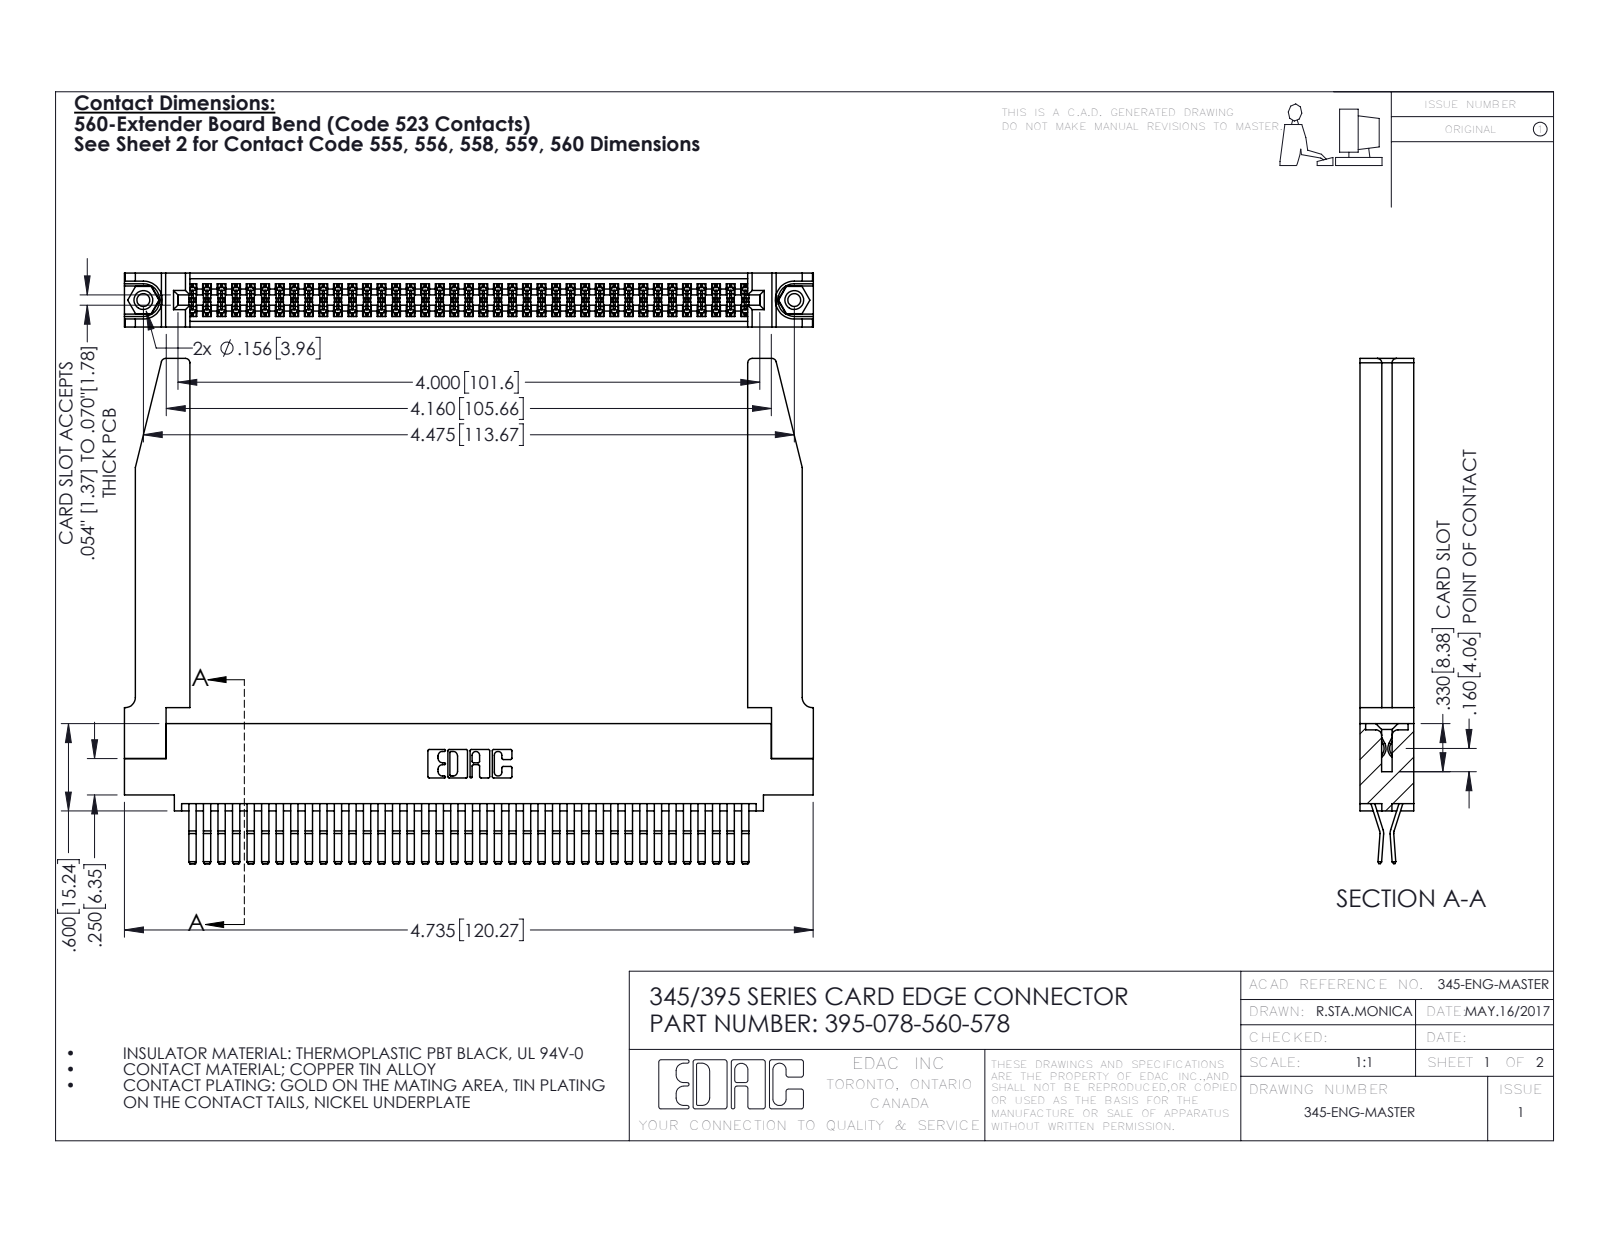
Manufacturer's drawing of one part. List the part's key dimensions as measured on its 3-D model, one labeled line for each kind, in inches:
Part name (STEP PRODUCT): 395-078-560-578; 345-292-001_560 Tail; 345-250-001_345-250-001-102; 345-220-078_345-220-078 (+1 more)
STEP written by: SolidWorks 2016 (CONFIG_CONTROL_DESIGN)
Units: inches
Bodies: 83 solids, 4420 faces (2800 planar, 1568 cylindrical, 52 other)
Overall size (bounding box): 4.736 × 3.472 × 0.37
Volume: 1.212 in³ · Surface area: 40.4 in²
Round holes (diameter × count): ⌀0.089 ×2, ⌀0.125 ×2, ⌀0.156 ×2, ⌀0.064 ×1
Round bosses / shafts (diameter × count): ⌀0.155 ×2
Partial cylindrical surfaces — rounded edges, fillets, slot ends (radius × count): R0.006 ×117, R0.01 ×22, R0.03 ×8, R0.007 ×6, R0.031 ×6, R0.026 ×3, R0.01 ×2, R0.014 ×2
Main face-to-face distances: 0.37, 0.072, 0.298, 0.025, 0.2, 0.098, 0.272, 0.225, 0.148, 0.15
Hole centre spacings: 0.27, 4.239, 4.475
